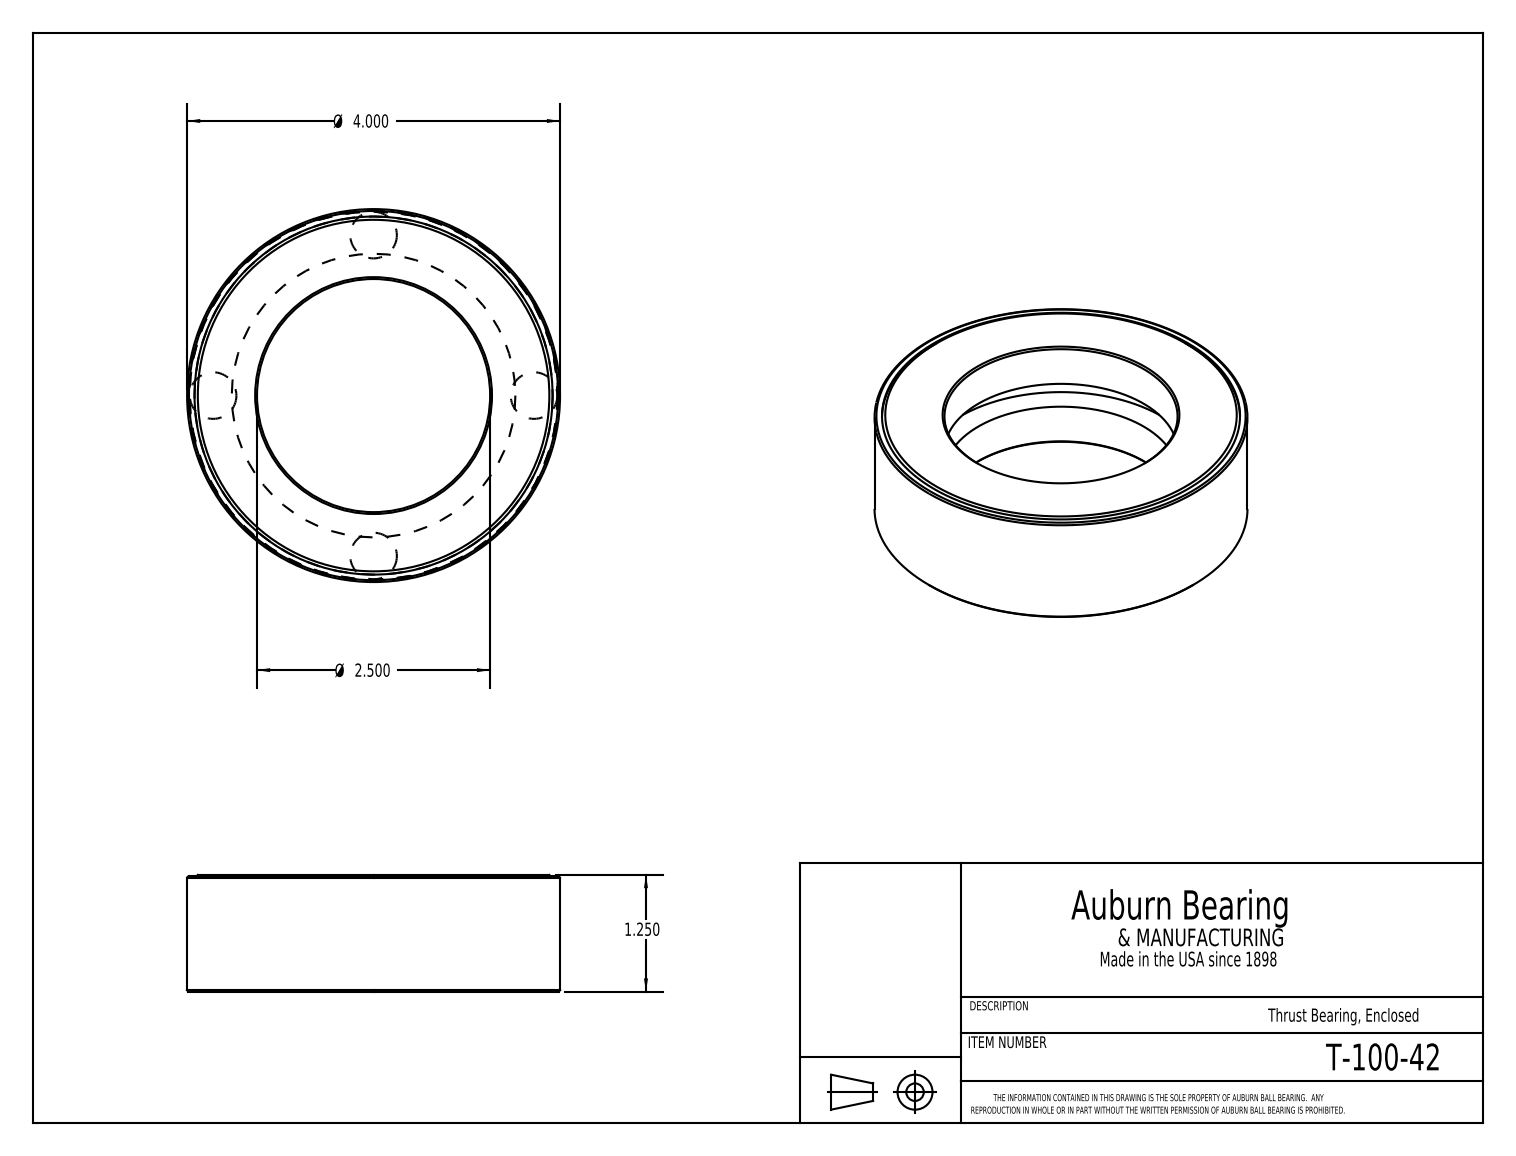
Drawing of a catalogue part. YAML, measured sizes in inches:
part_name: "T-100-42"
step_written_by: "SolidWorks 2016 (CONFIG_CONTROL_DESIGN)"
units: inches
bodies: {solids: 6, faces: 28, planar: 9, cylindrical: 7, other: 12}
overall_size: [4, 4, 1.25]
volume: 6.924
surface_area: 73.3
round_holes:
  - {diameter: 2.5, count: 1}
  - {diameter: 3.84, count: 1}
  - {diameter: 3.96, count: 1}
round_bosses_or_shafts:
  - {diameter: 4, count: 1}
  - {diameter: 3.946, count: 1}
face_to_face_distances: [1.25, 0.475, 0.775, 0.3, 1.215, 1.235, 0.74, 0.76, 0.44, 0.46]
